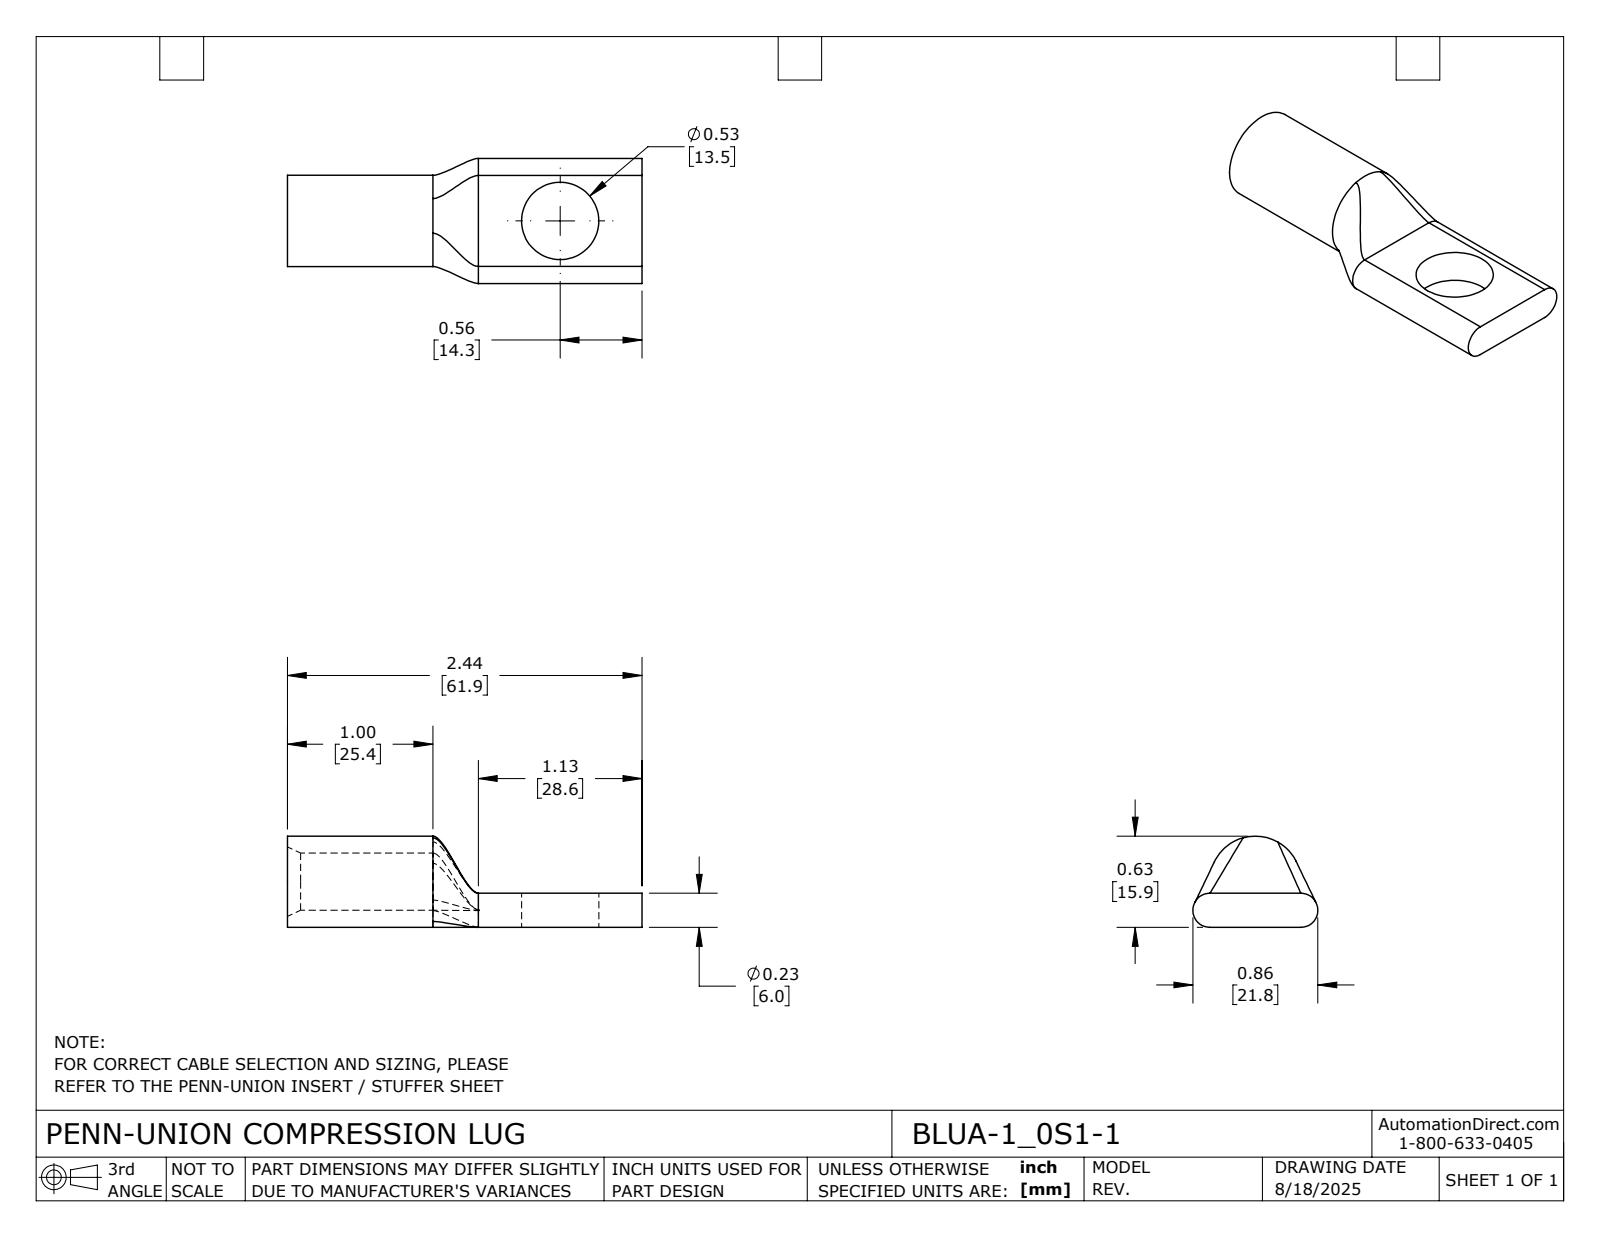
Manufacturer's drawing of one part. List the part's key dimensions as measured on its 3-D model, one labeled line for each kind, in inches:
Part name (STEP PRODUCT): BLUA-1_0S1-1
STEP written by: SolidWorks 2024 (CONFIG_CONTROL_DESIGN)
Units: inches
Bodies: 1 solid, 24 faces (5 planar, 9 cylindrical, 10 other)
Overall size (bounding box): 2.438 × 0.859 × 0.627
Volume: 0.405 in³ · Surface area: 6.939 in²
Round holes (diameter × count): ⌀0.393 ×1, ⌀0.531 ×1
Round bosses / shafts (diameter × count): ⌀0.627 ×1
Partial cylindrical surfaces — rounded edges, fillets, slot ends (radius × count): R0.117 ×2
Main face-to-face distances: 0.234, 2.437, 1.313, 1.125
